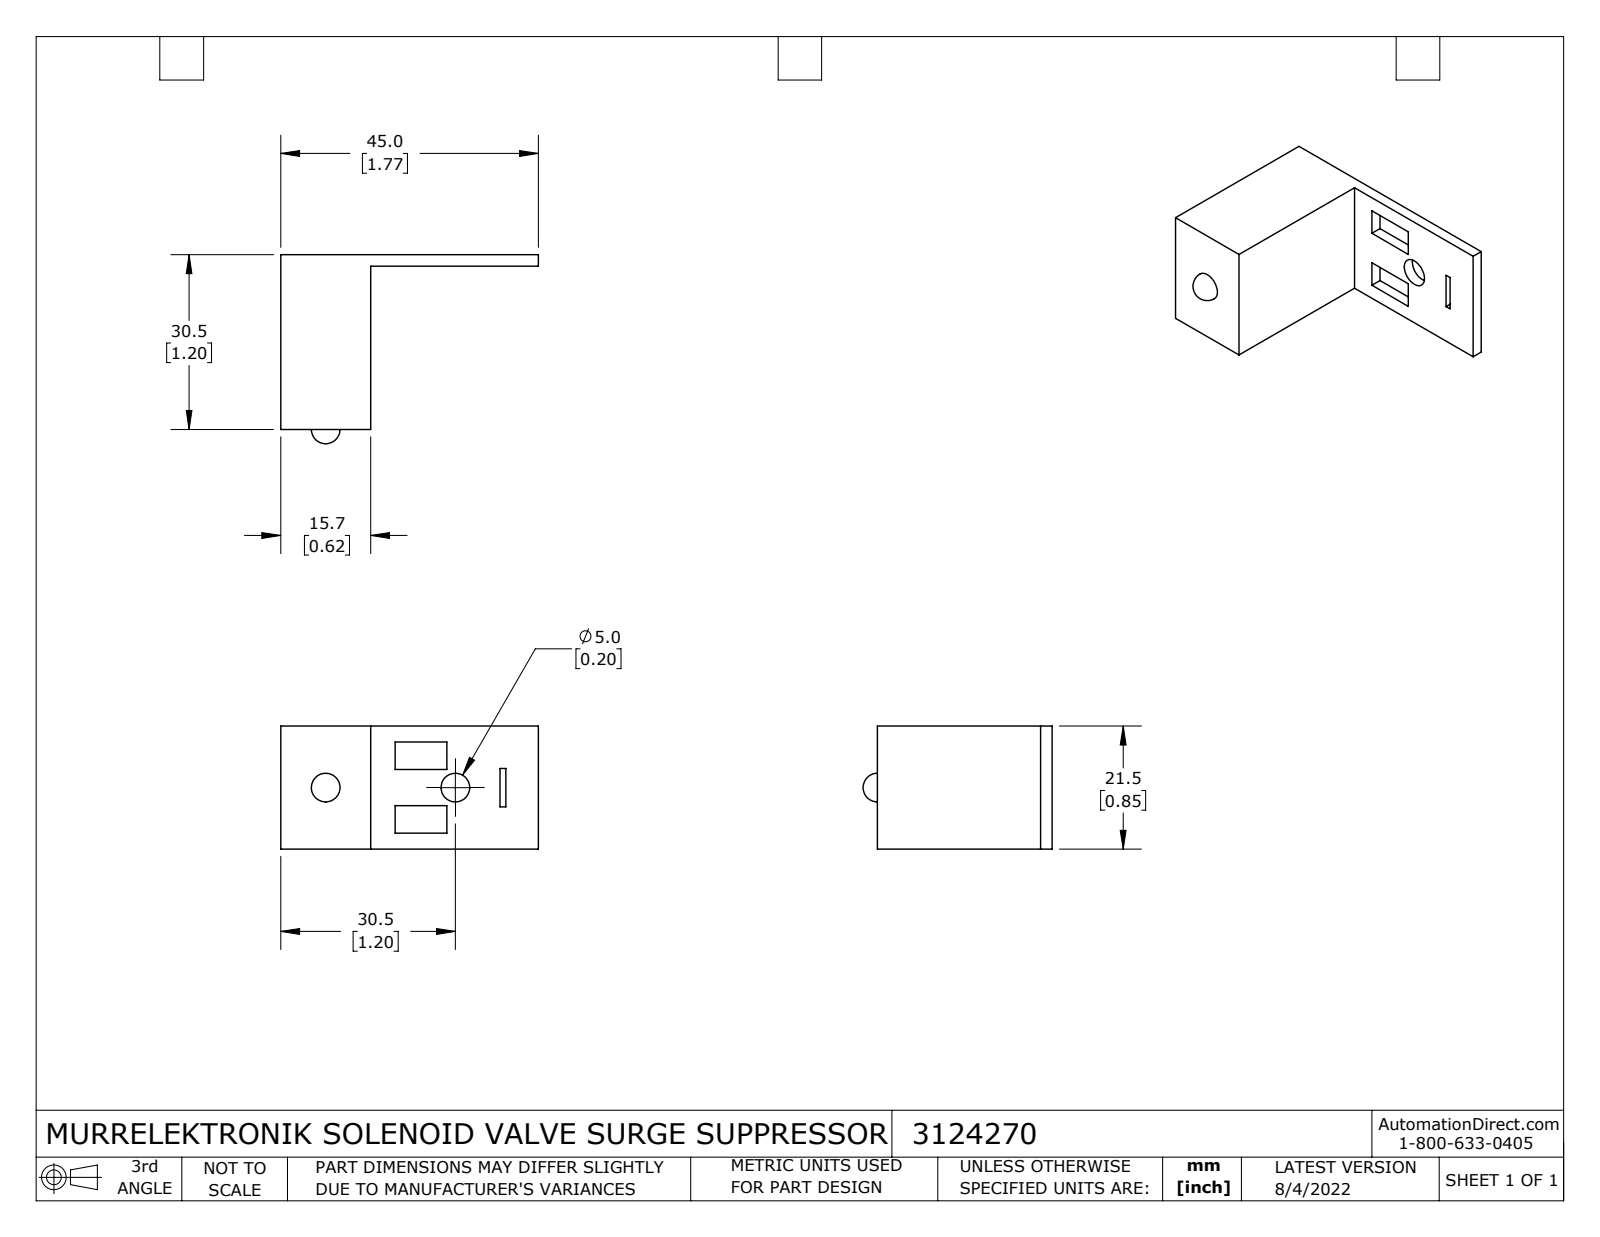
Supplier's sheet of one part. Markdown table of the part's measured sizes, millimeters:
| quantity | value |
| --- | --- |
| part name | 3124270 |
| STEP written by | SolidWorks 2021 (CONFIG_CONTROL_DESIGN) |
| units | millimeters |
| bodies | 1 solid, 24 faces (20 planar, 2 cylindrical, 2 other) |
| overall size | 45 × 33 × 21.5 |
| volume | 11 362 mm³ |
| surface area | 4 288 mm² |
| round holes (diameter × count) | 5 × 1 |
| main face-to-face distances | 15.7, 21.5, 2, 30.5, 28.5, 29.3, 45, 2.8, 7.6, 13.9 |
